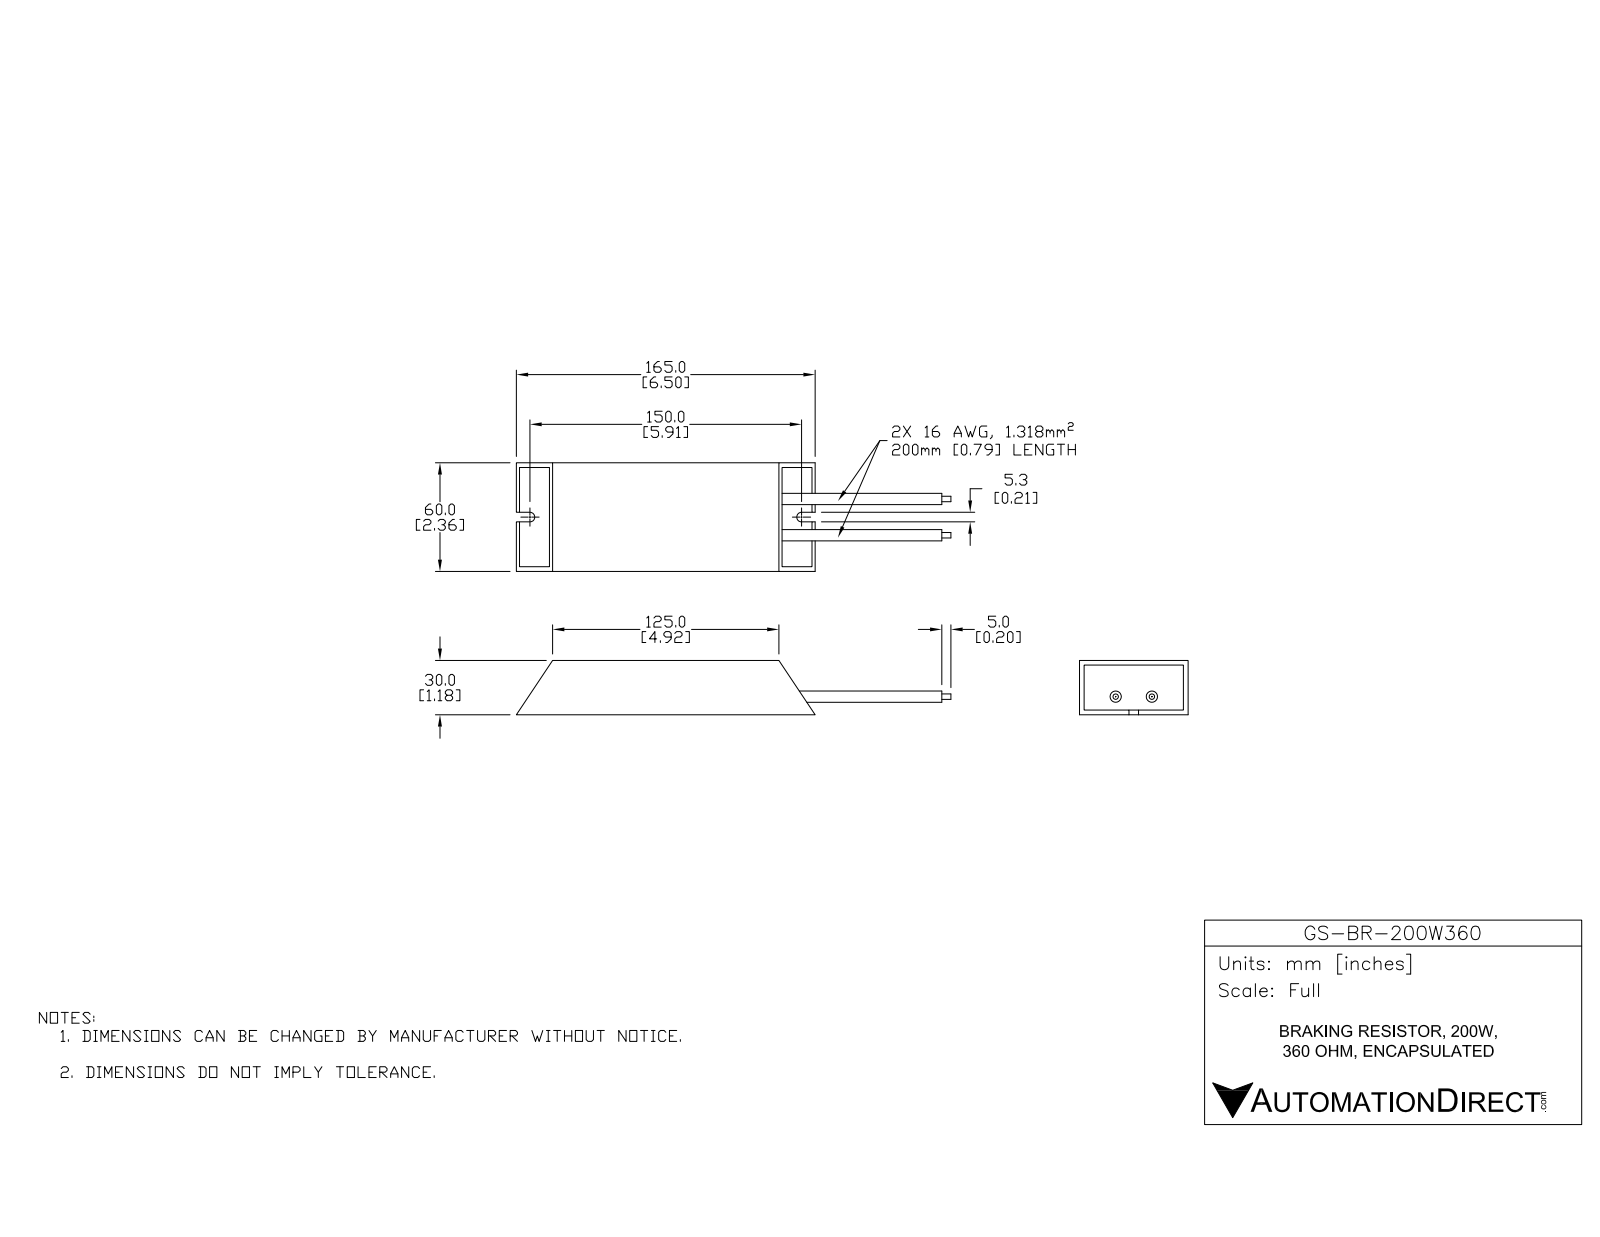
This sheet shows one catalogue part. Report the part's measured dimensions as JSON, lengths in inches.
{"part_name": "GS-BR-200W360", "step_written_by": "SolidWorks 2015 (AUTOMOTIVE_DESIGN)", "units": "inches", "bodies": {"solids": 1, "faces": 34, "planar": 24, "cylindrical": 10, "other": 0}, "overall_size": [9.449, 2.362, 1.181], "volume_in3": 14.59, "surface_area_in2": 56.66, "round_bosses_or_shafts": [[0.244, 2], [0.118, 2]], "partial_cylinders_radius": [[0.104, 2]], "face_to_face_distances": [1.181, 2.362, 0.102, 1.079, 4.921, 2.26, 2.157, 0.976, 1.077, 1.285]}
